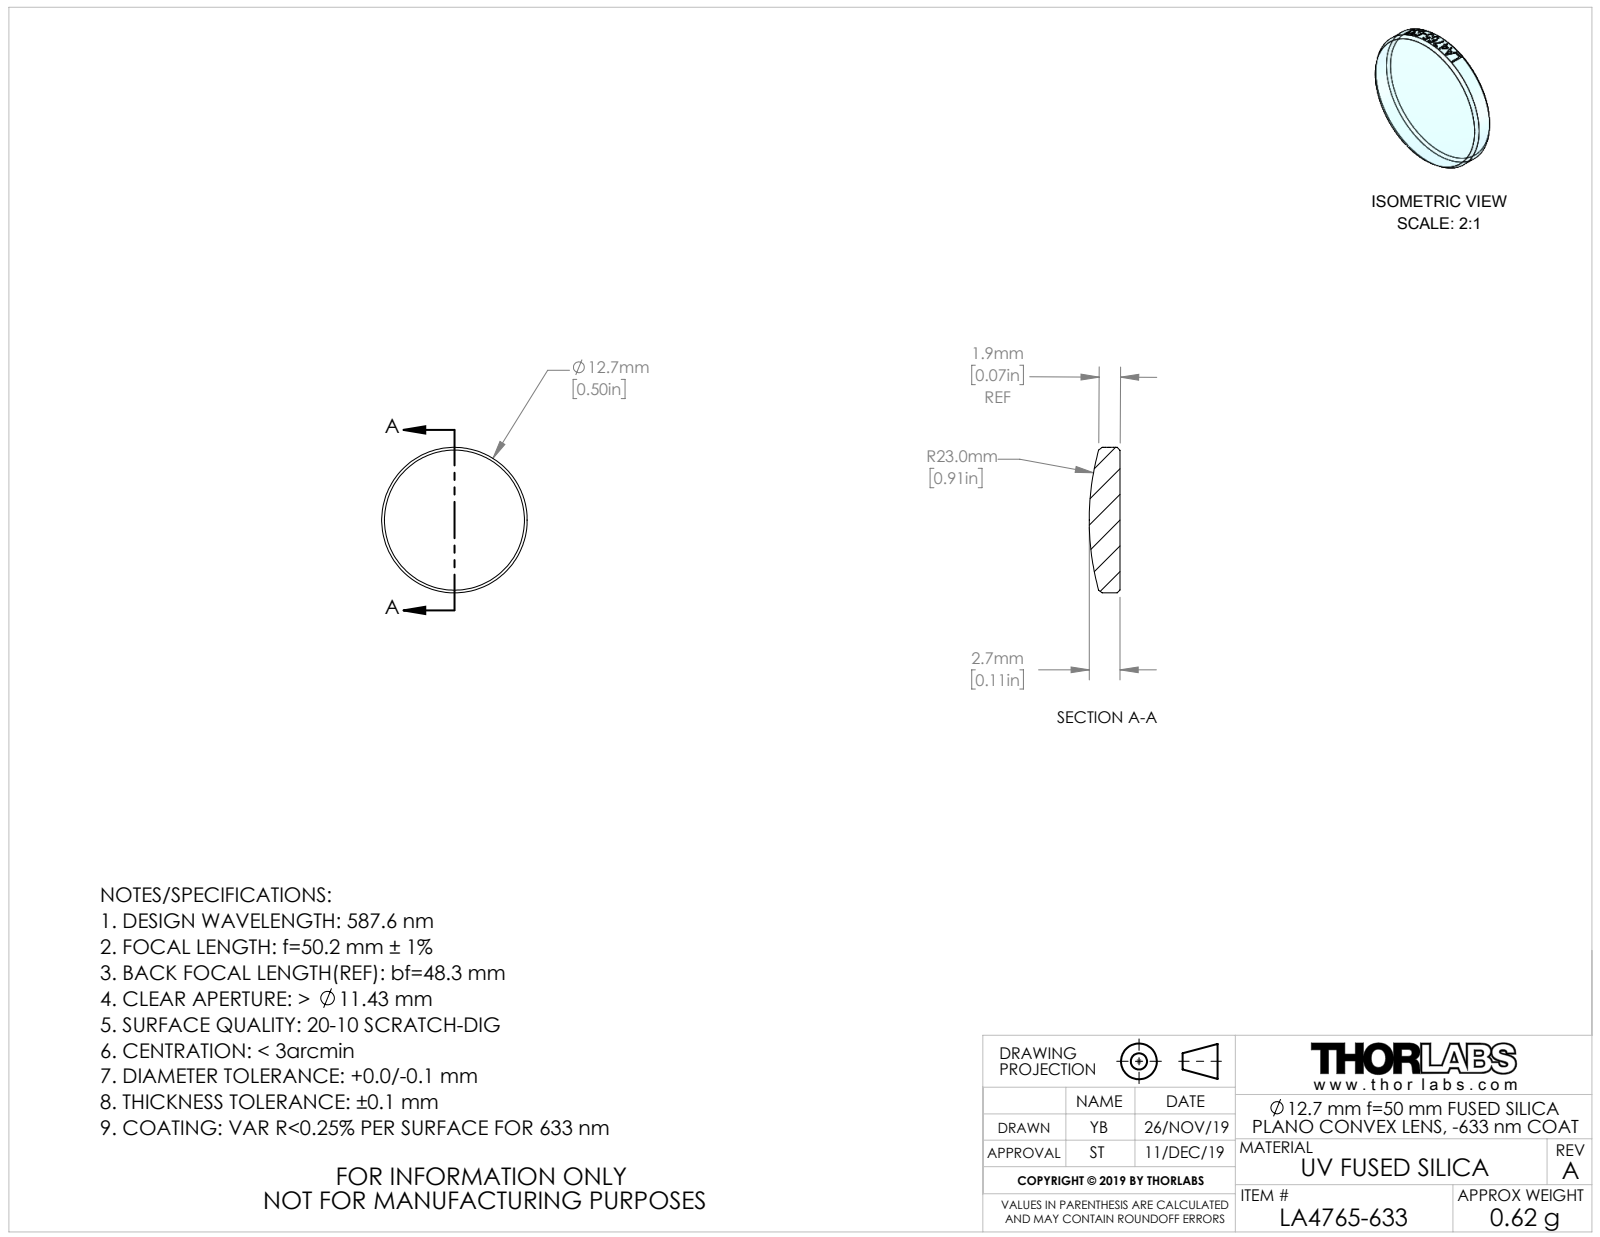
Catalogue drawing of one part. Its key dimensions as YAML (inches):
part_name: "CTN015005; CTN014986-999"
step_written_by: "SolidWorks 2018 (AUTOMOTIVE_DESIGN)"
units: inches
bodies: {solids: 1, faces: 23, planar: 1, cylindrical: 16, other: 6}
overall_size: [0.5, 0.5, 0.106]
volume: 0.017
surface_area: 0.493
round_bosses_or_shafts:
  - {diameter: 0.5, count: 1}
